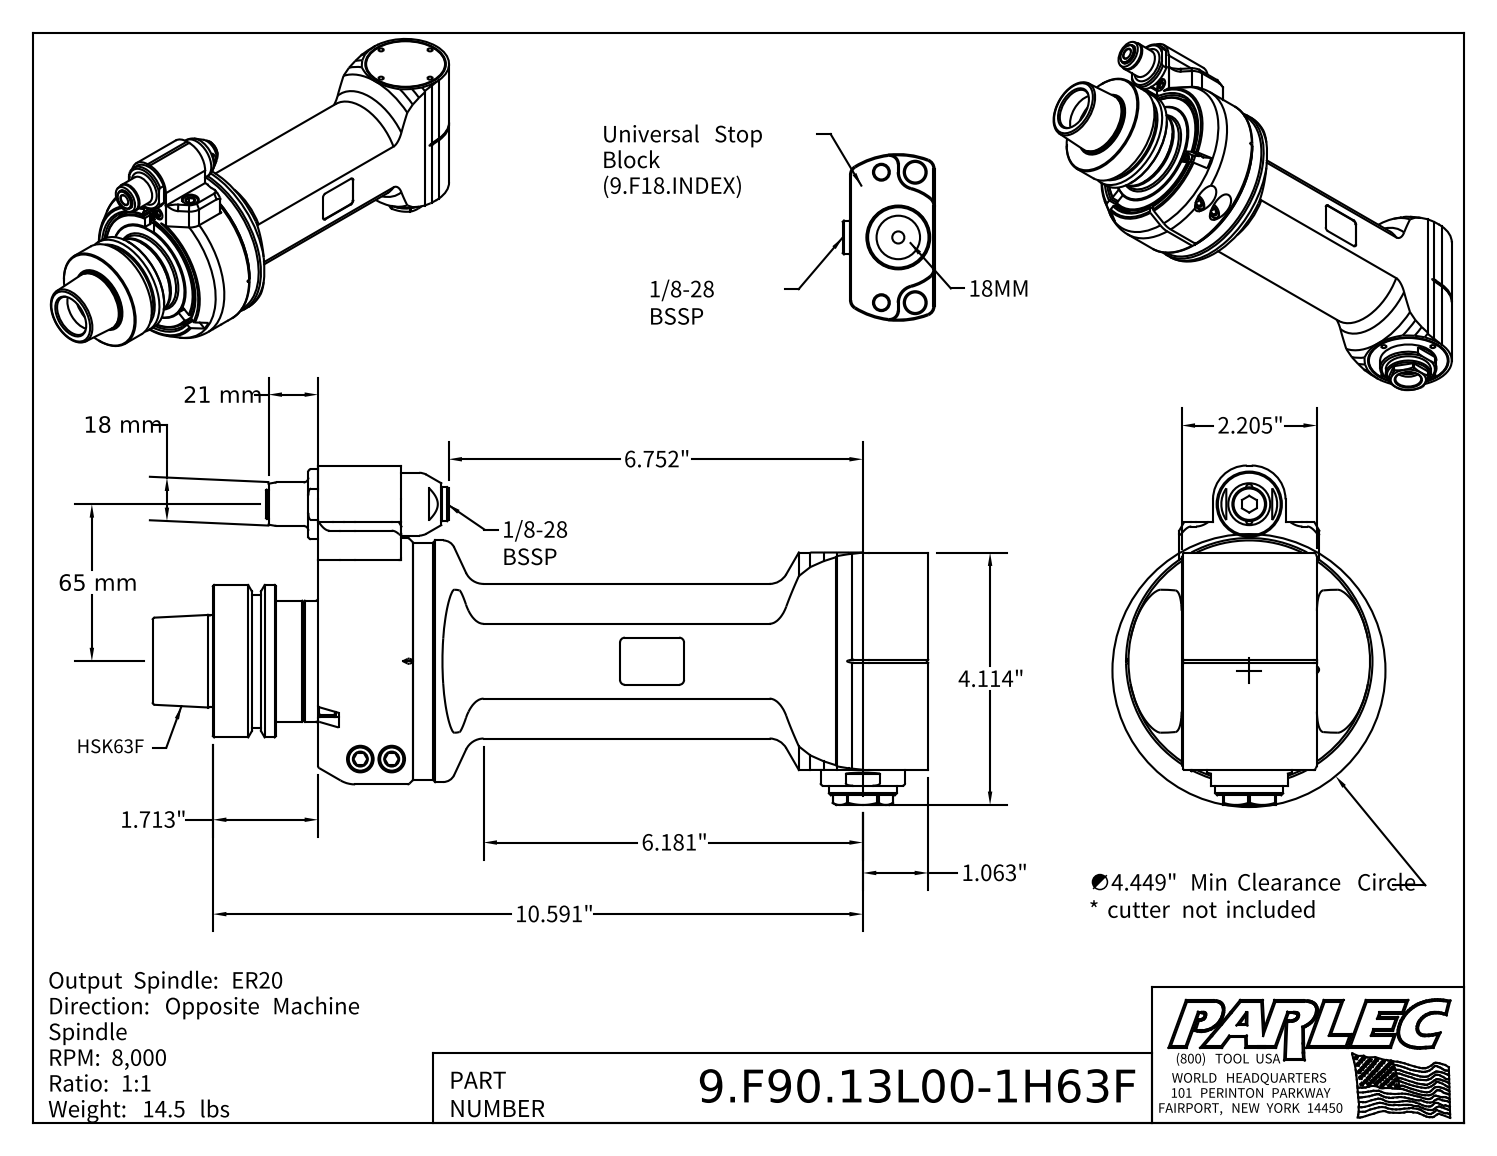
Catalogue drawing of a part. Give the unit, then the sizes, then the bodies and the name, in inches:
Units: inches
Overall size (bounding box): 12.638 × 5.531 × 4.016
Round holes (diameter × count): ⌀0.126 ×4, ⌀0.256 ×3, ⌀0.102 ×2, ⌀0.13 ×2, ⌀0.165 ×2, ⌀0.197 ×2, ⌀0.315 ×2, ⌀0.409 ×2, ⌀0.433 ×2, ⌀0.492 ×2, ⌀1.142 ×2, ⌀0.098 ×1
Round bosses / shafts (diameter × count): ⌀0.394 ×4, ⌀0.709 ×2, ⌀0.472 ×2, ⌀0.315 ×2, ⌀0.236 ×2, ⌀0.098 ×2, ⌀4.016 ×1, ⌀3.937 ×1
Partial cylindrical surfaces — rounded edges, fillets, slot ends (radius × count): R0.039 ×14, R0.079 ×12, R0.118 ×6, R0.157 ×4, R0.016 ×2, R0.02 ×2, R0.315 ×2, R0.551 ×2
Main face-to-face distances: 1.26, 2.205, 1.024, 0.02, 0.276, 0.335, 0.039, 2.047, 1.713, 1.555
Hole centre spacings: 0.846, 1.197, 0.276, 0.504, 0.74, 0.848, 0.996, 1.693
Volume: 76.97 in³ · Surface area: 241.7 in²
Bodies: 4 solids, 600 faces (264 planar, 154 cylindrical, 182 other)
Part name (STEP PRODUCT): 9.F90.13L00-1H63F; 9GA11C_C66 (Type 1, HSK63F, 65mm); 9_F90_13L00
STEP written by: Autodesk Inventor 2020 (AUTOMOTIVE_DESIGN)
